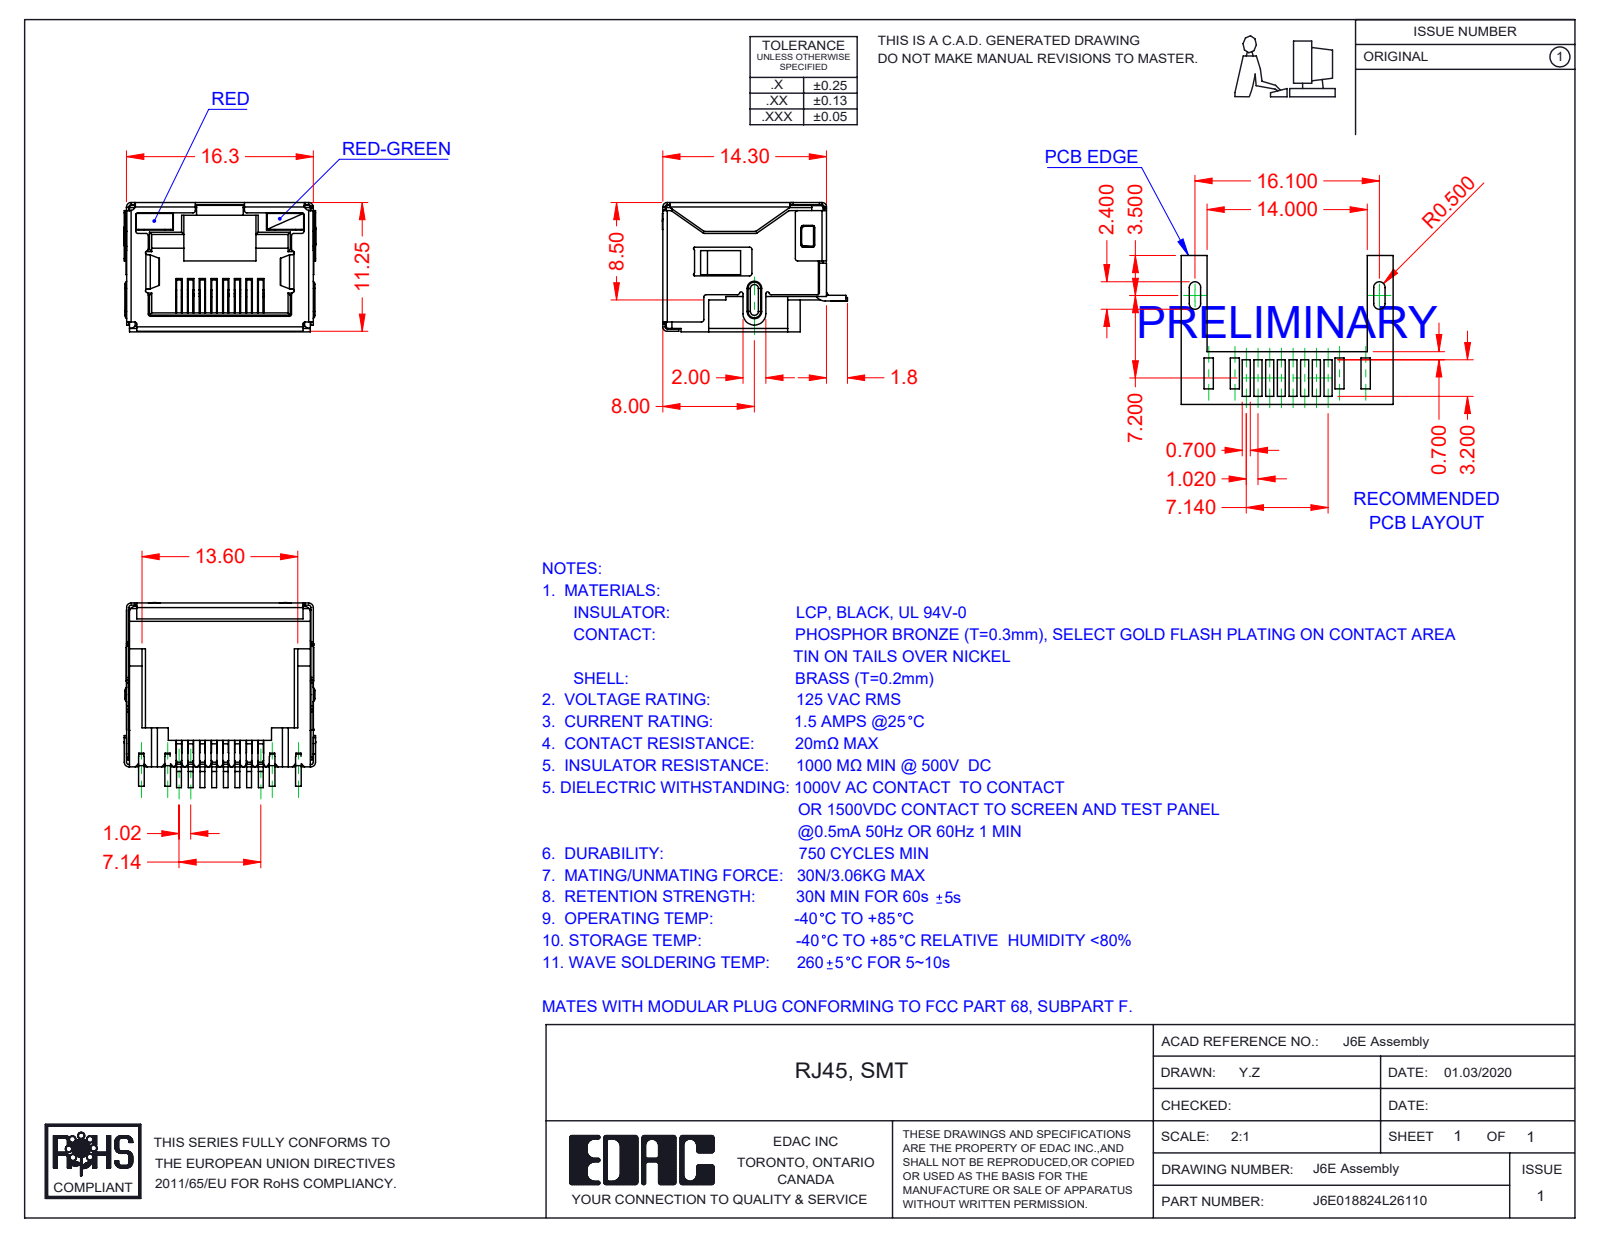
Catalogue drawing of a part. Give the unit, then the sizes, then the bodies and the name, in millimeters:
Units: millimetres
Overall size (bounding box): 16.75 × 16.15 × 11.3
Partial cylindrical surfaces — rounded edges, fillets, slot ends (radius × count): R0.2 ×82, R0.25 ×17, R0.4 ×13, R0.5 ×13, R0.1 ×10, R0.15 ×7, R0.3 ×4, R1 ×3
Main face-to-face distances: 11.05, 16.05, 16.1, 15.85, 11.1, 11.3, 2.4, 0.7, 9.85, 0.49
Volume: 1 109 mm³ · Surface area: 4 045 mm²
Bodies: 12 solids, 1498 faces (1099 planar, 349 cylindrical, 50 other)
Part name (STEP PRODUCT): 6E Contacts; 6E LED RH_6-Red-Green; 6E LED LH_2-Red; 6E Insulator_LED (+2 more)
STEP written by: SolidWorks 2016 (CONFIG_CONTROL_DESIGN)
